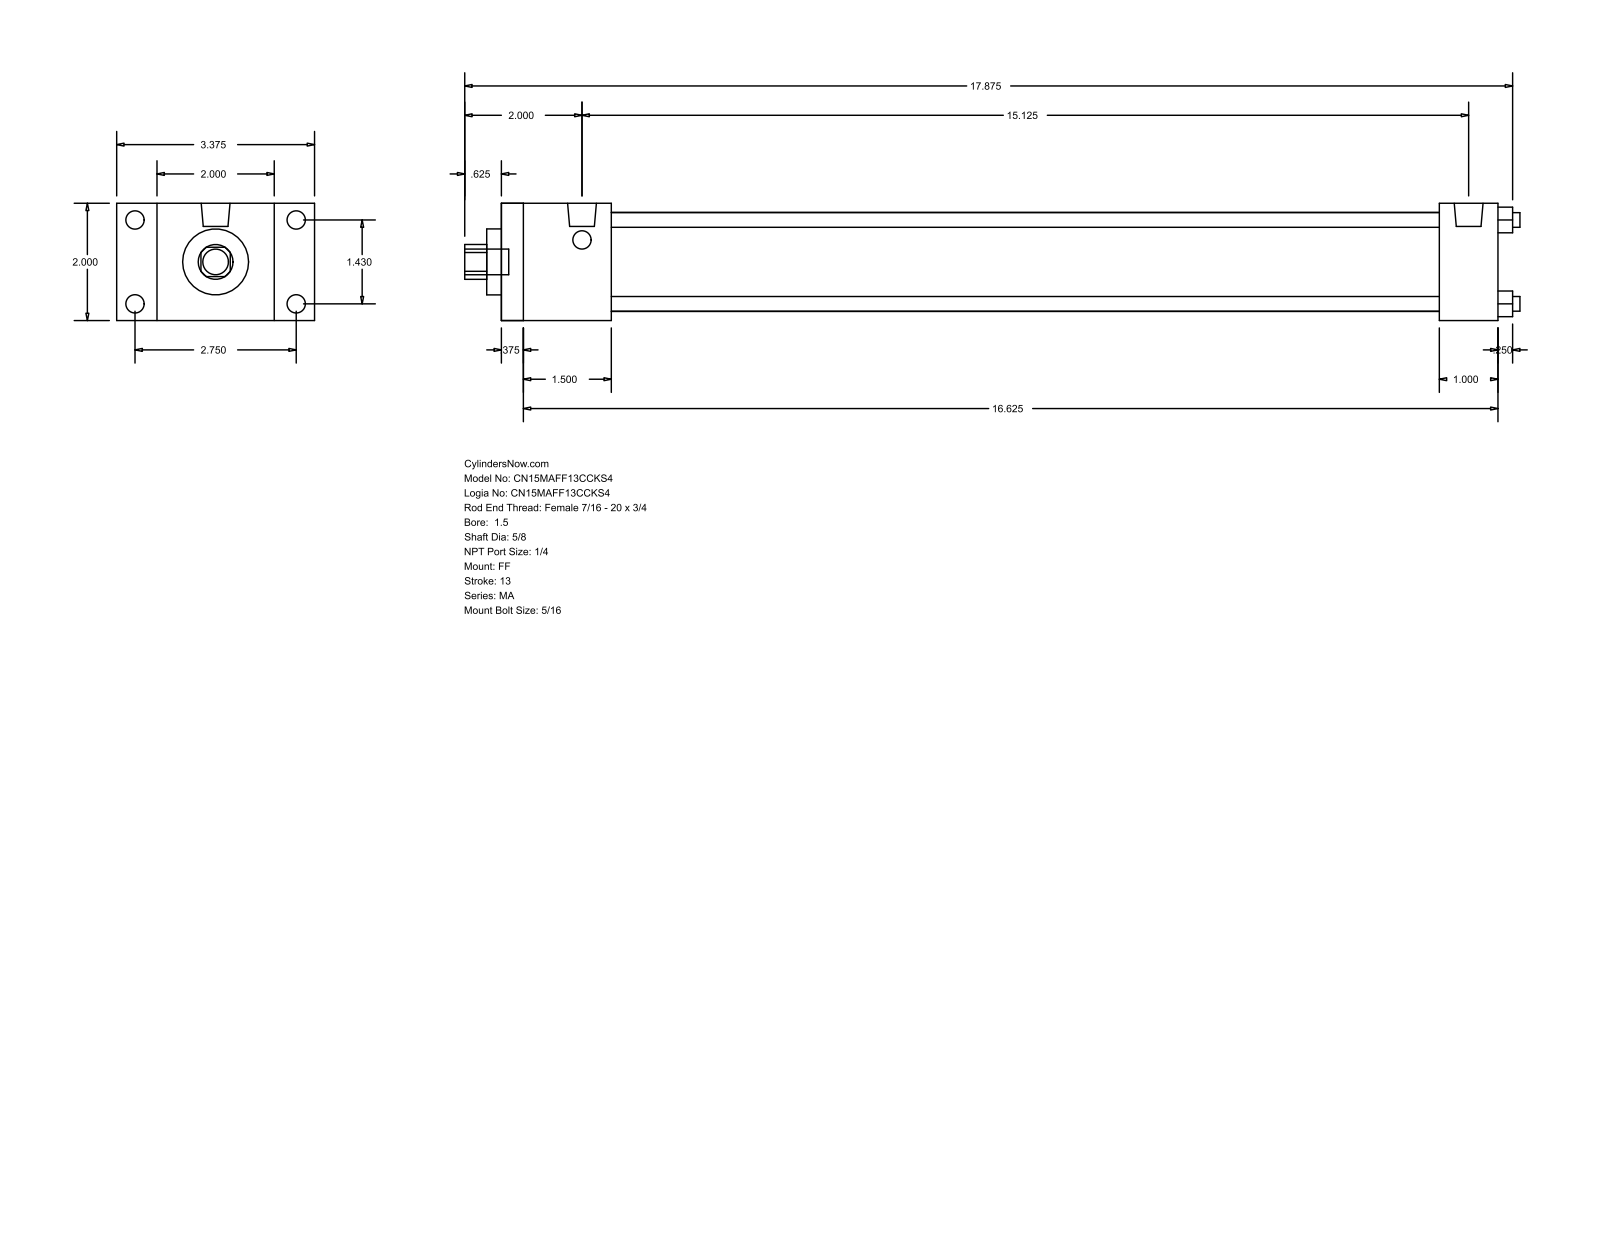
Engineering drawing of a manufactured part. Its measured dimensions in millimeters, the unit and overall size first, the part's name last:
Units: millimetres
Overall size (bounding box): 457.2 × 85.72 × 50.8
Round holes (diameter × count): ⌀6.35 ×4, ⌀15.88 ×1, ⌀28.57 ×1, ⌀42.93 ×1
Round bosses / shafts (diameter × count): ⌀7.94 ×8, ⌀12.49 ×2, ⌀11.11 ×1
Partial cylindrical surfaces — rounded edges, fillets, slot ends (radius × count): R7.54 ×1
Main face-to-face distances: 50.8, 431.8, 9.52, 422.28, 47.62, 406.39, 38.1, 396.87, 358.77, 384.18
Hole centre spacings: 25.68, 36.32, 51.36
Bodies: 0 solids, 92 faces (64 planar, 28 cylindrical, 0 other)
Part name (STEP PRODUCT): MA_FF__0150_0.625
STEP written by: GSSL Pune (CONFIG_CONTROL_DESIGN)
